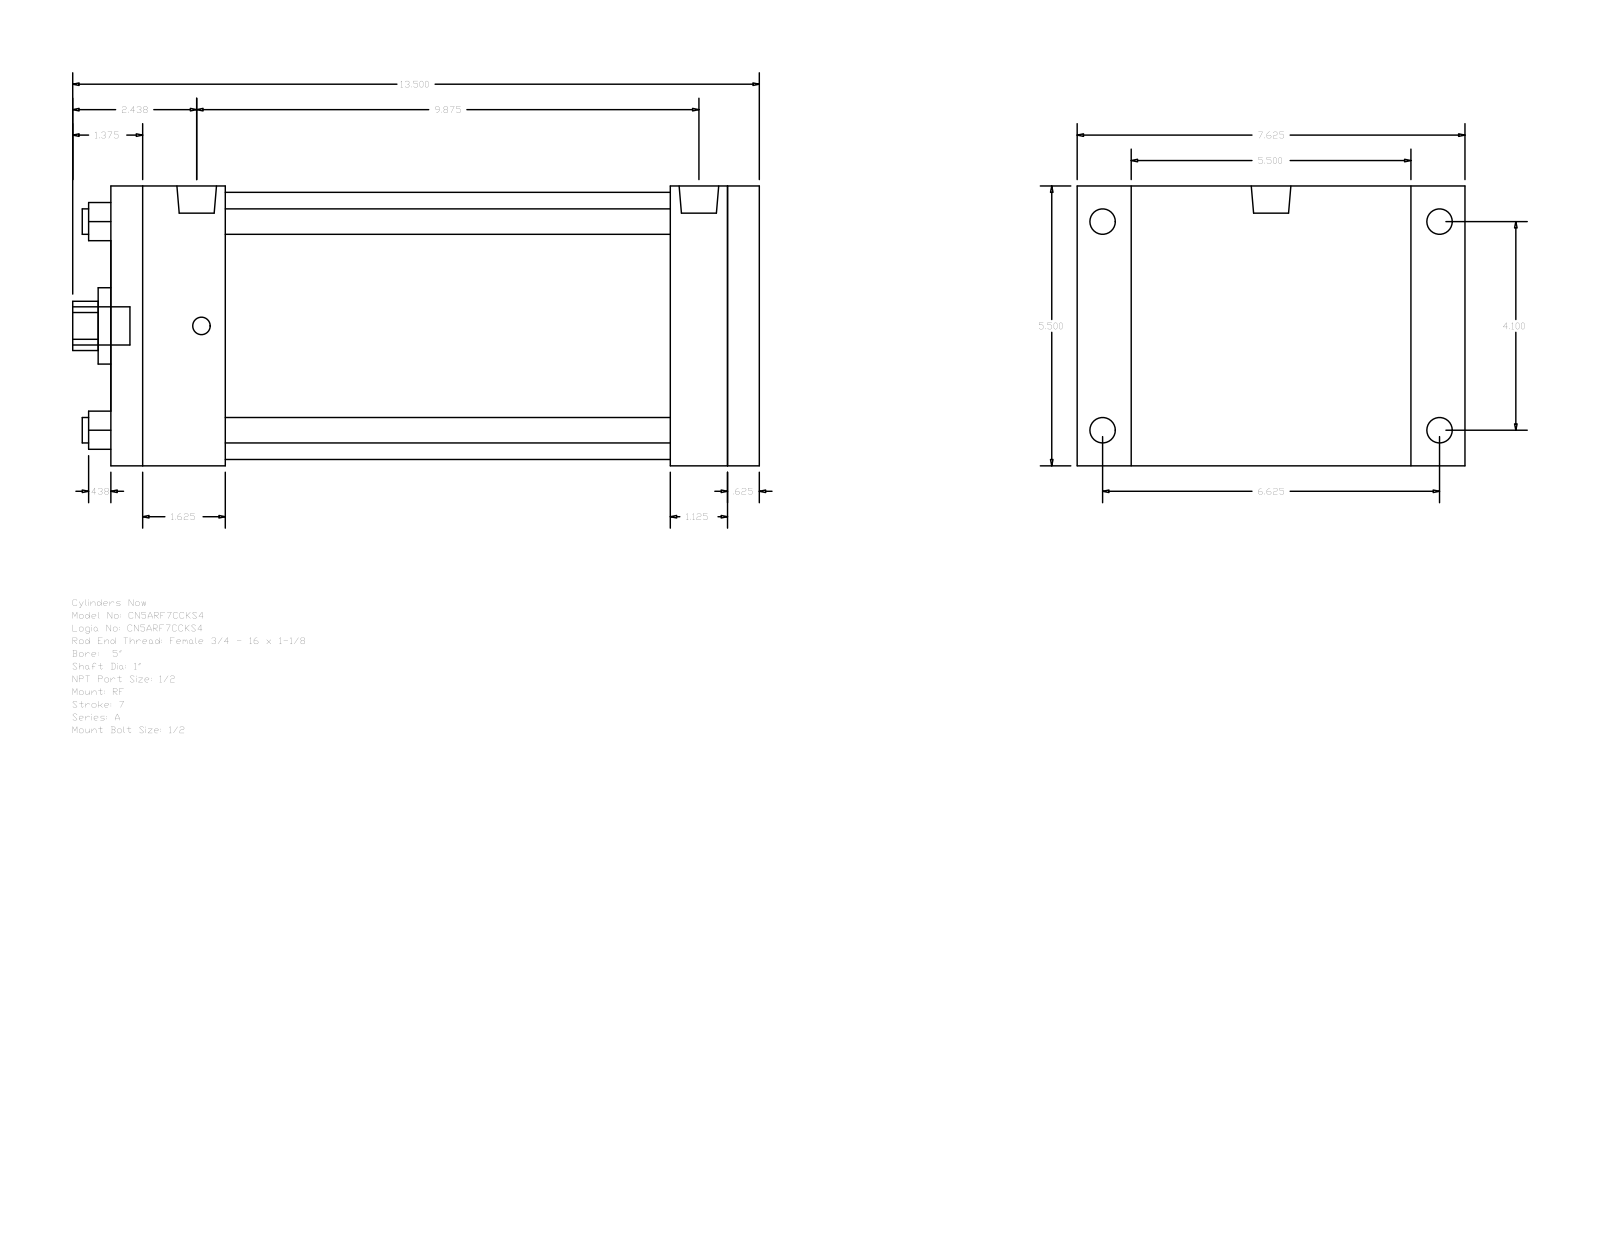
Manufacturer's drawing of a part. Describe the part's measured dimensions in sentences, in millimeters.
The part is named "A_RF__0500_1". Its 3-D file was written by "GSSL Pune (CONFIG_CONTROL_DESIGN)". It is 0 solids with 92 faces: 64 planar, 28 cylindrical and 0 other. Overall it measures 342.9 by 193.68 by 139.7 millimeters. Round holes: 4 of diameter 12.7, 1 of diameter 25.4, 1 of diameter 38.1, 1 of diameter 133.35. Round bosses or shafts: 4 of diameter 12.7, 4 of diameter 8.73, 2 of diameter 19.77, 1 of diameter 19.05. Partial cylindrical surfaces (rounded edges, fillets, slot ends): 1 of radius 12.29. The main face-to-face distances are 139.7, 323.85, 307.97, 15.88, 28.57, 57.15, 250.82, 266.7, 279.4, 222.25. The hole center spacings are 73.64, 104.14, 147.28.
